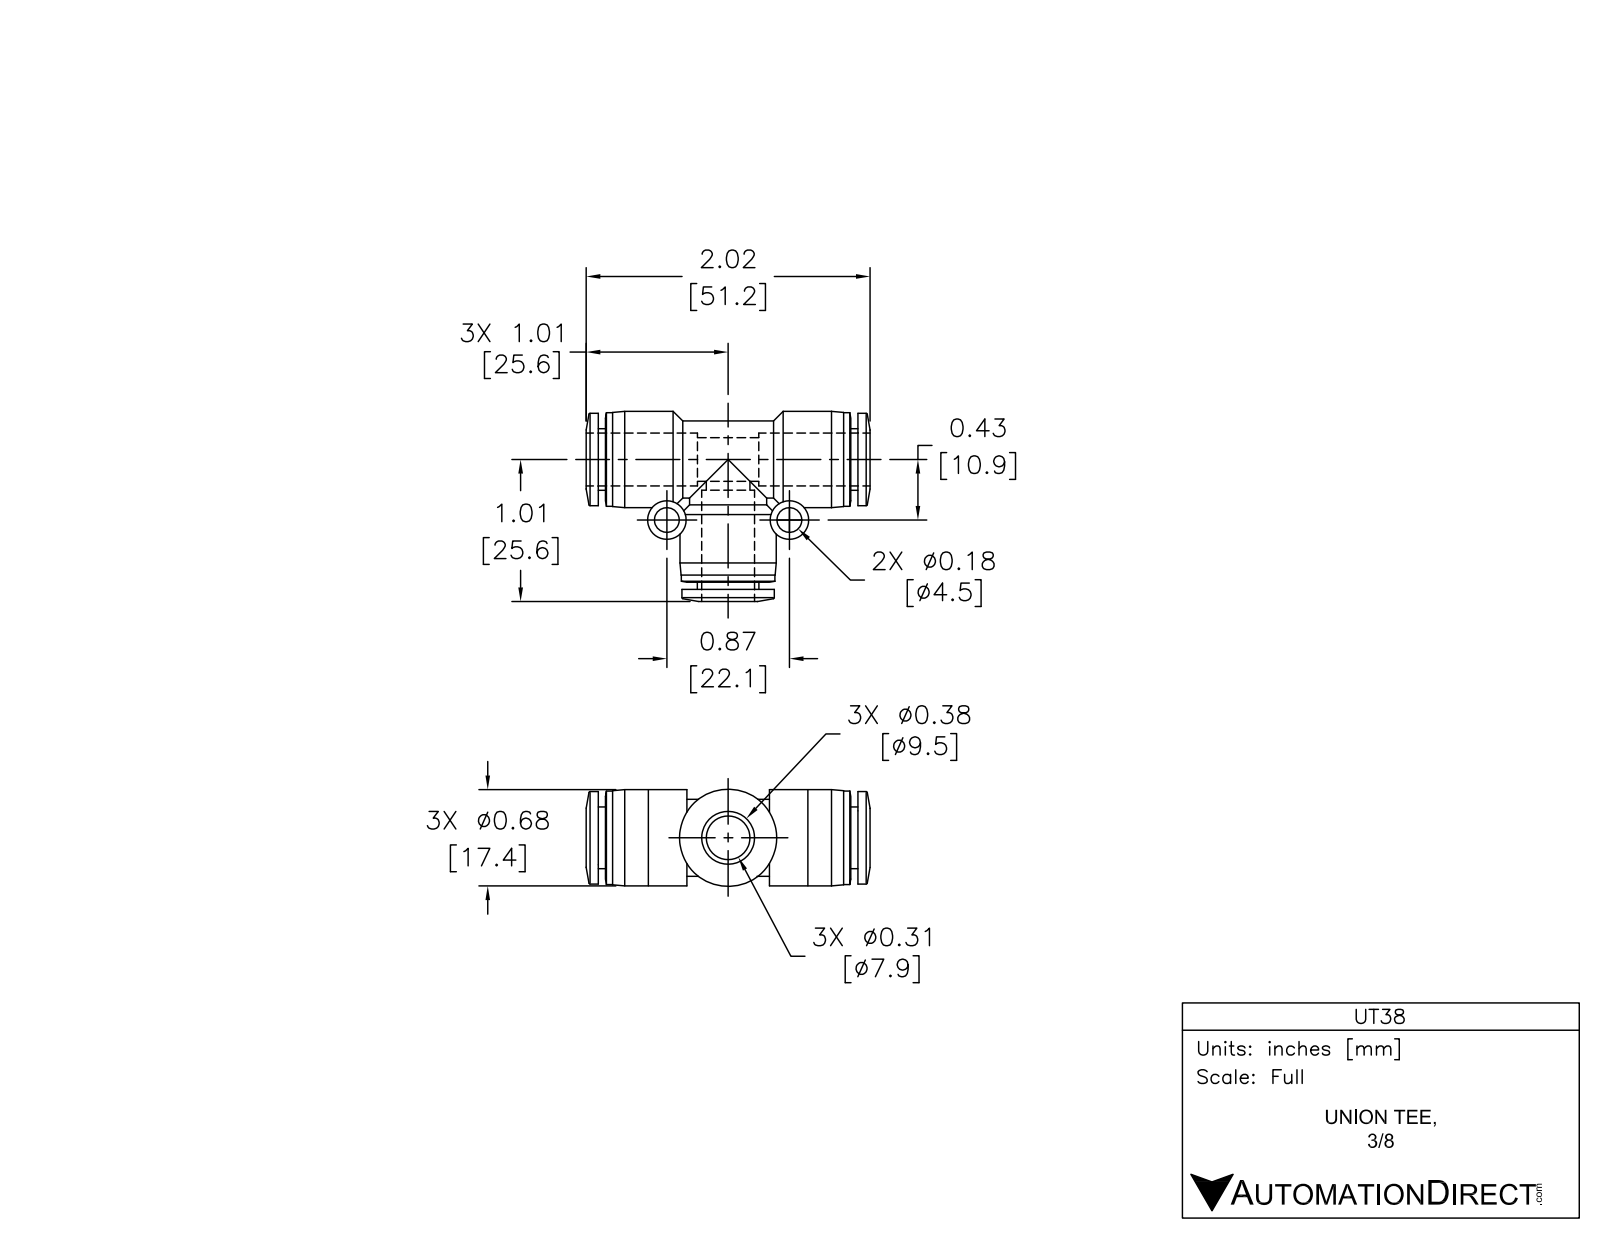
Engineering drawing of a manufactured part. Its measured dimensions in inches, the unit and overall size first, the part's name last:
Units: inches
Overall size (bounding box): 2.031 × 1.36 × 0.689
Round holes (diameter × count): ⌀0.177 ×2, ⌀0.315 ×2, ⌀0.386 ×2
Round bosses / shafts (diameter × count): ⌀0.689 ×2, ⌀0.669 ×2, ⌀0.661 ×2, ⌀0.551 ×2, ⌀0.441 ×2, ⌀0.276 ×2
Main face-to-face distances: 0.051, 1.807, 1.858, 1.756, 0.705, 0.654, 1.154, 1.102, 0.689, 0.449
Hole centre spacings: 0.866
Volume: 0.603 in³ · Surface area: 12.3 in²
Bodies: 1 solid, 104 faces (16 planar, 46 cylindrical, 42 other)
Part name (STEP PRODUCT): UT38
STEP written by: SolidWorks 2015 (AUTOMOTIVE_DESIGN)
